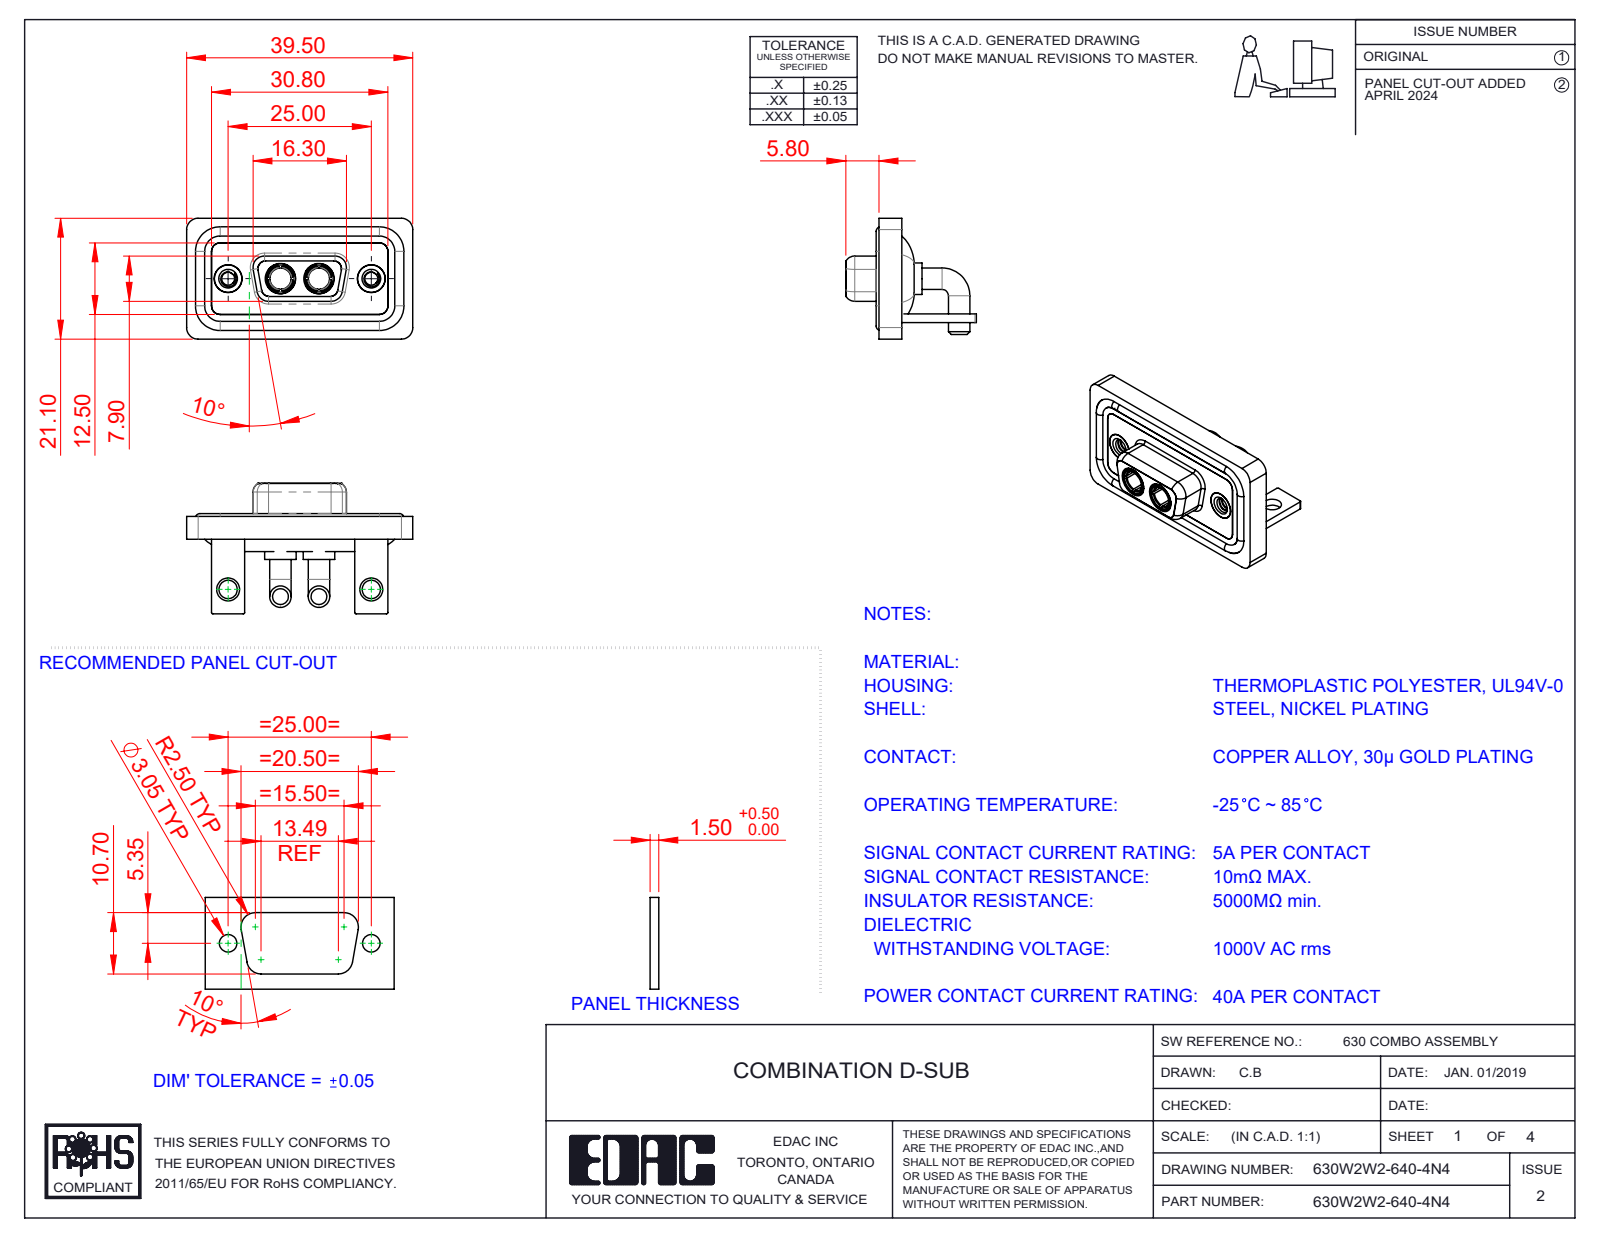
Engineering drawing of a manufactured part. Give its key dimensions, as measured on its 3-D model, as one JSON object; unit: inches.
{"part_name": "Power Socket_40A RA; 630Combo Housing_2W2; 630Combo Shell Rear_09 Contacts; 630Combo Waterproof Housing_09 Contacts (+4 more)", "step_written_by": "SolidWorks 2023 (CONFIG_CONTROL_DESIGN)", "units": "inches", "bodies": {"solids": 13, "faces": 590, "planar": 183, "cylindrical": 262, "other": 145}, "overall_size": [1.555, 0.898, 0.831], "volume_in3": 0.325, "surface_area_in2": 13.34, "round_holes": [[0.191, 4], [0.089, 2], [0.126, 2], [0.146, 2], [0.157, 2], [0.159, 2], [0.197, 2], [0.209, 2]], "round_bosses_or_shafts": [[0.148, 4], [0.063, 4], [0.217, 2], [0.205, 2], [0.195, 2], [0.195, 2], [0.189, 2], [0.187, 2]], "partial_cylinders_radius": [[0.079, 19], [0.059, 18], [0.01, 16], [0.053, 8], [0.063, 8], [0.02, 5], [0.024, 4], [0.026, 4]], "face_to_face_distances": [0.016, 0.114, 0.059, 0.071, 0.043, 0.146, 0.031, 0.098, 0.063, 0.122], "hole_center_spacings": [0.36, 0.624, 0.984, 0.265]}
